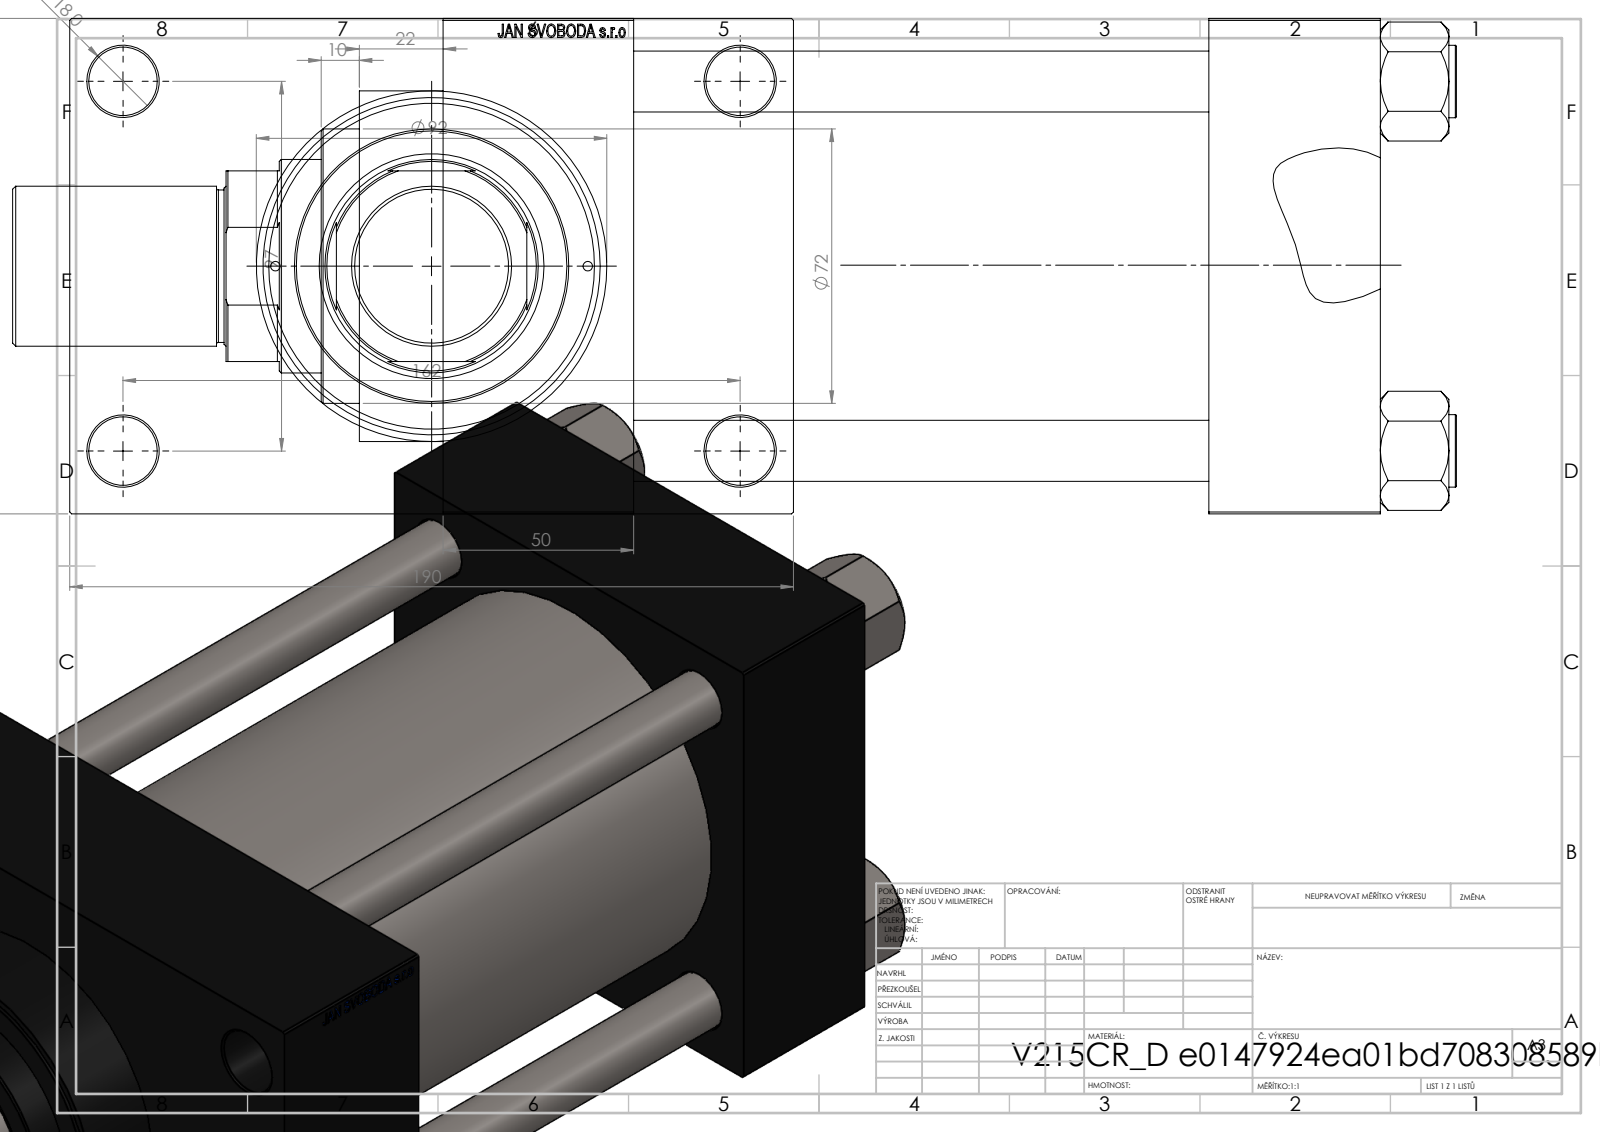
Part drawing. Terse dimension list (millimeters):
name: V215_VC_A; V215CR_VCP_D; V215CR_D_TYCINKA; NUT_M5_D (+2 more)
written by: SolidWorks 2019 (CONFIG_CONTROL_DESIGN)
unit: mm
bodies: 12 solids, 1173 faces (551 planar, 96 cylindrical, 526 other)
size: 379 × 190 × 130
volume: 3 044 000 mm³; area: 454 418 mm²
holes: 4× ⌀16, 4× ⌀18, 2× ⌀2.5, 2× ⌀7, 2× ⌀26.44, 2× ⌀35, 1× ⌀40.5, 1× ⌀56, 1× ⌀59, 1× ⌀76, 1× ⌀85.5, 1× ⌀100
bosses: 4× ⌀19, 1× ⌀106, 1× ⌀92, 1× ⌀72, 1× ⌀42, 1× ⌀40
rounds: 1× R27
face distances: 130, 50, 45, 196, 151, 246, 201, 30, 160, 150
hole spacings: 32.55, 49.02, 62.87, 68.52, 94.41, 96.9, 101.73, 102.27
